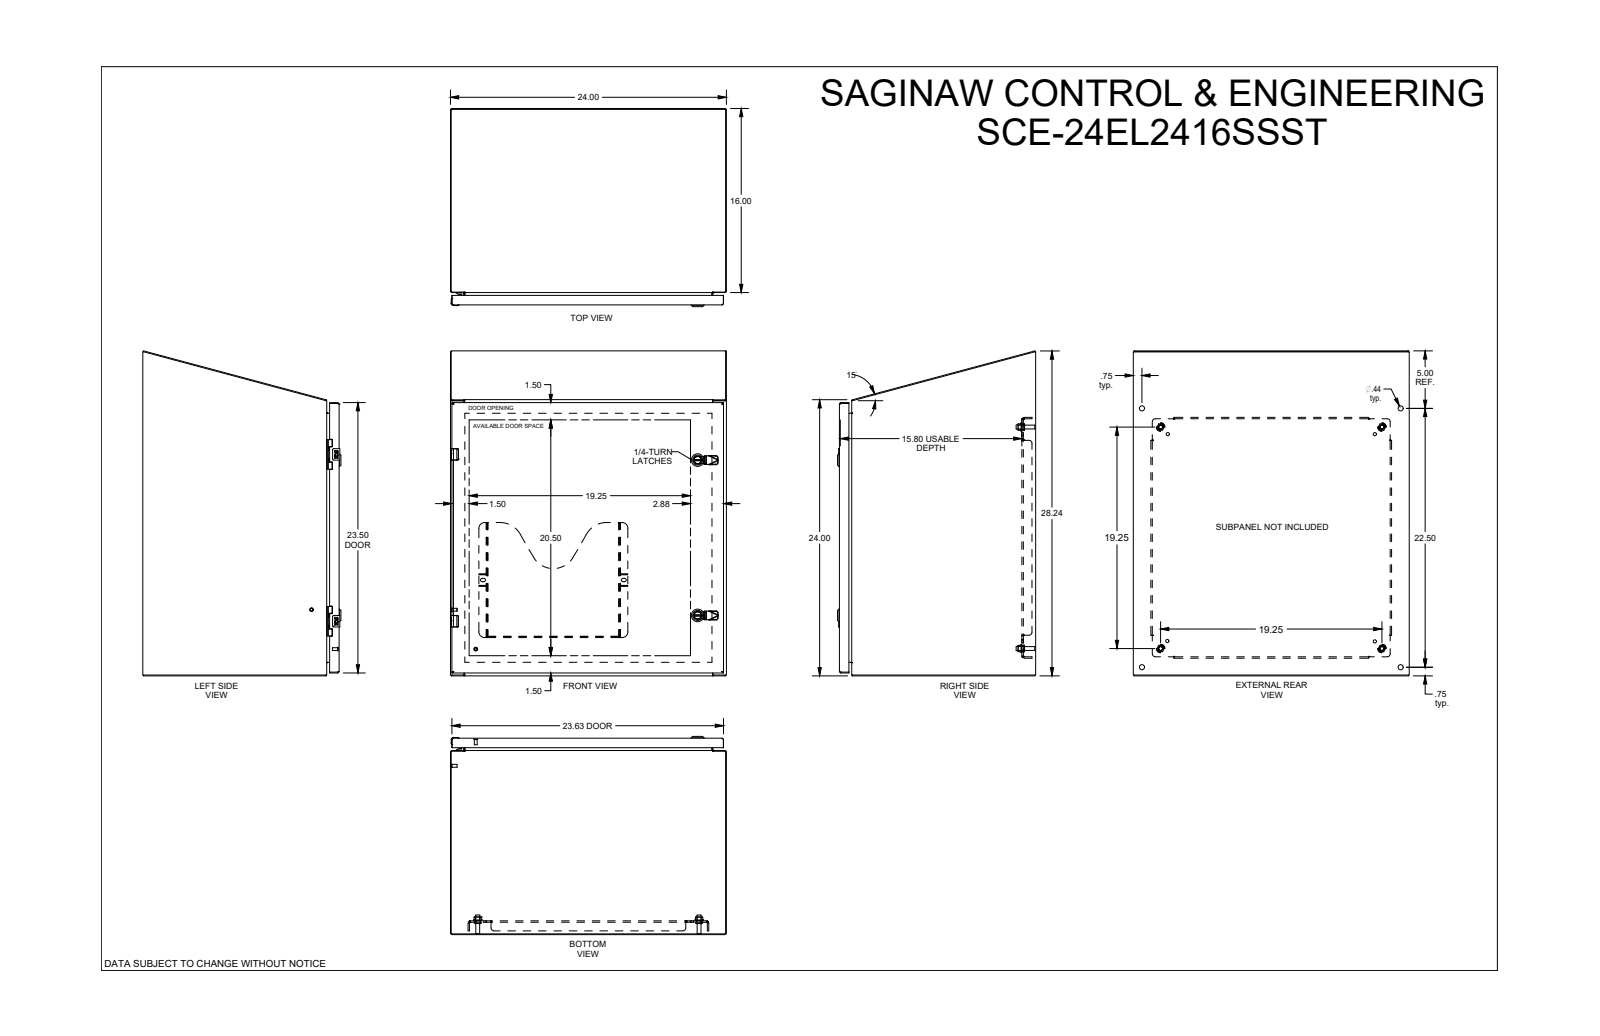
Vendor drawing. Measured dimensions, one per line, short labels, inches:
name: SCE-24EL2416SSST
written by: SolidWorks 2019 (CONFIG_CONTROL_DESIGN)
unit: in
bodies: 0 solids, 2844 faces (1311 planar, 759 cylindrical, 774 other)
size: 28.249 × 24 × 17.23
holes: 4× ⌀0.172, 4× ⌀0.205, 4× ⌀0.244, 4× ⌀0.266, 4× ⌀0.281, 4× ⌀0.367, 4× ⌀0.437, 4× ⌀0.5, 2× ⌀0.156, 2× ⌀0.197, 2× ⌀0.218, 2× ⌀0.25
bosses: 6× ⌀0.17, 4× ⌀0.366, 4× ⌀0.332, 4× ⌀0.25, 4× ⌀0.248, 3× ⌀0.196, 2× ⌀1.102, 2× ⌀0.866
rounds: 56× R0.012, 32× R0.015, 28× R0.01, 23× R0.04, 20× R0.02, 12× R0.029, 11× R0.06, 10× R0.07
face distances: 0.075, 23.925, 0.075, 16.998, 16.923, 17.073, 16.998, 1.2, 15.873, 1
hole spacings: 14.5, 0.985, 20.38, 20.938, 18.641, 0.02, 0.875, 4.493
